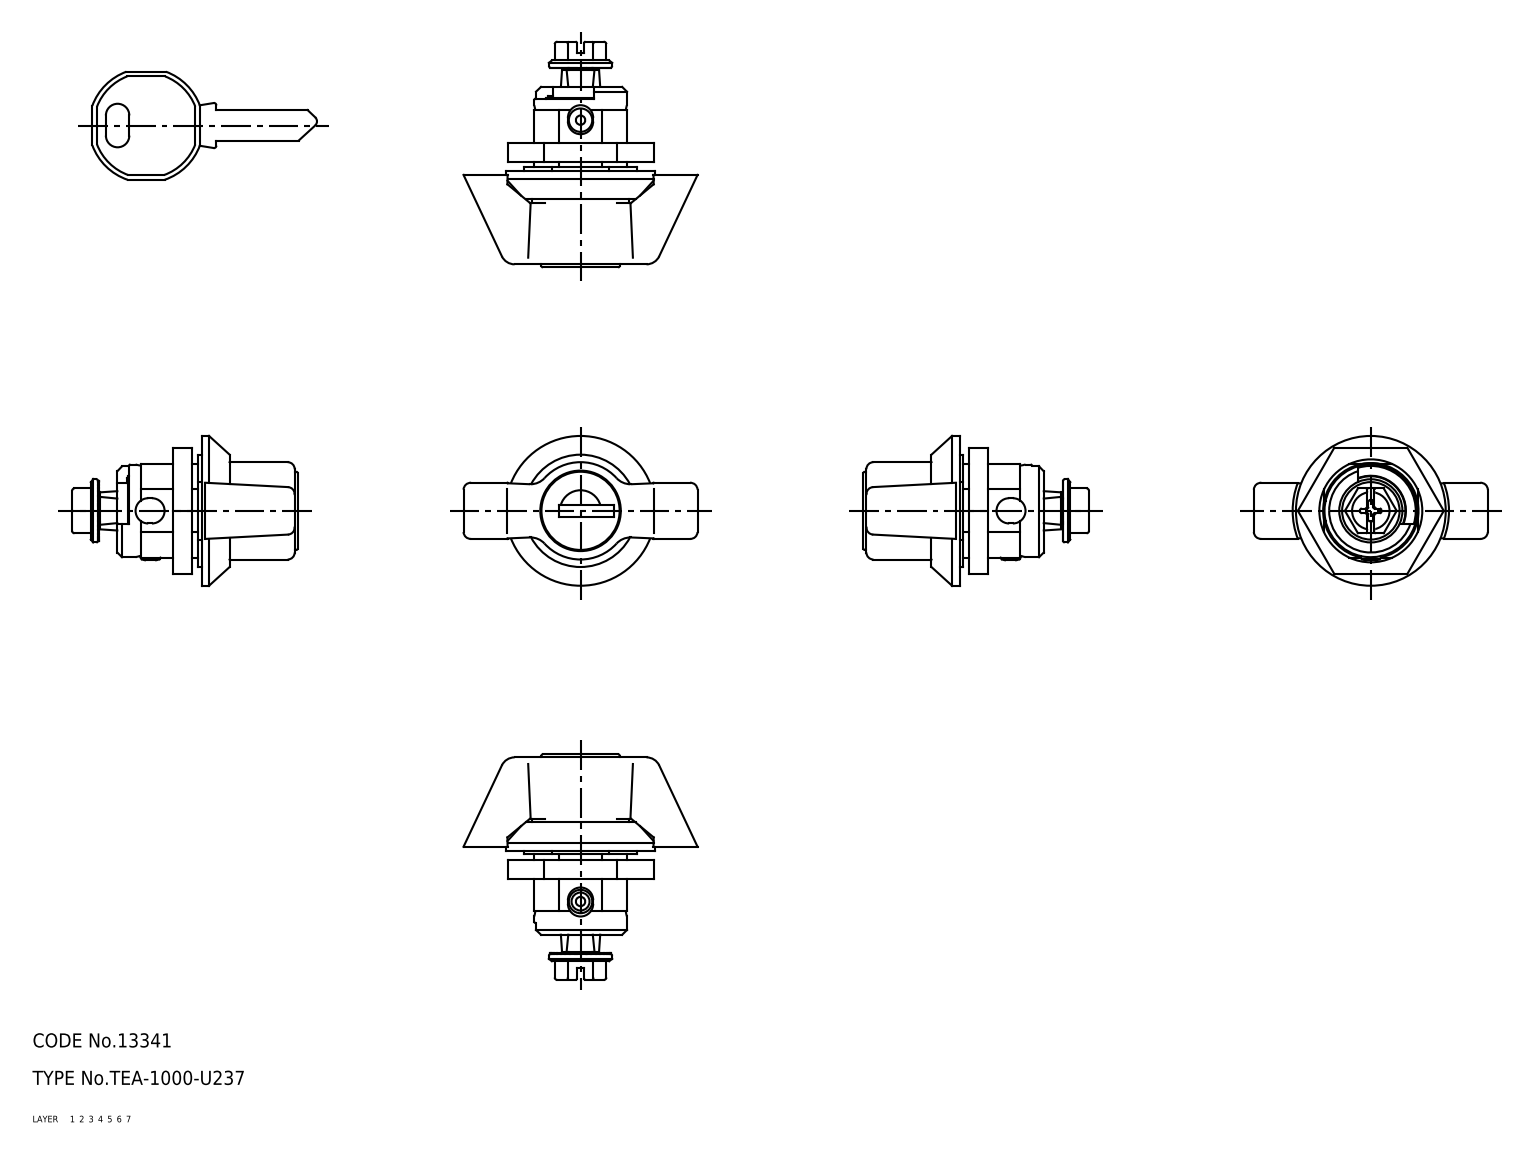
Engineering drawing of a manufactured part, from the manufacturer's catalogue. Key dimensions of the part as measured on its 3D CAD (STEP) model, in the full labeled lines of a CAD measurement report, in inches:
Part name (STEP PRODUCT): nut; lock; key; housing (+2 more)
STEP written by: CADfix (AUTOMOTIVE_DESIGN)
Units: inches
Bodies: 5 solids, 319 faces (0 planar, 0 cylindrical, 319 other)
Overall size (bounding box): 4.8 × 1.969 × 1.26
Volume: 1.329 in³ · Surface area: 20.61 in²
